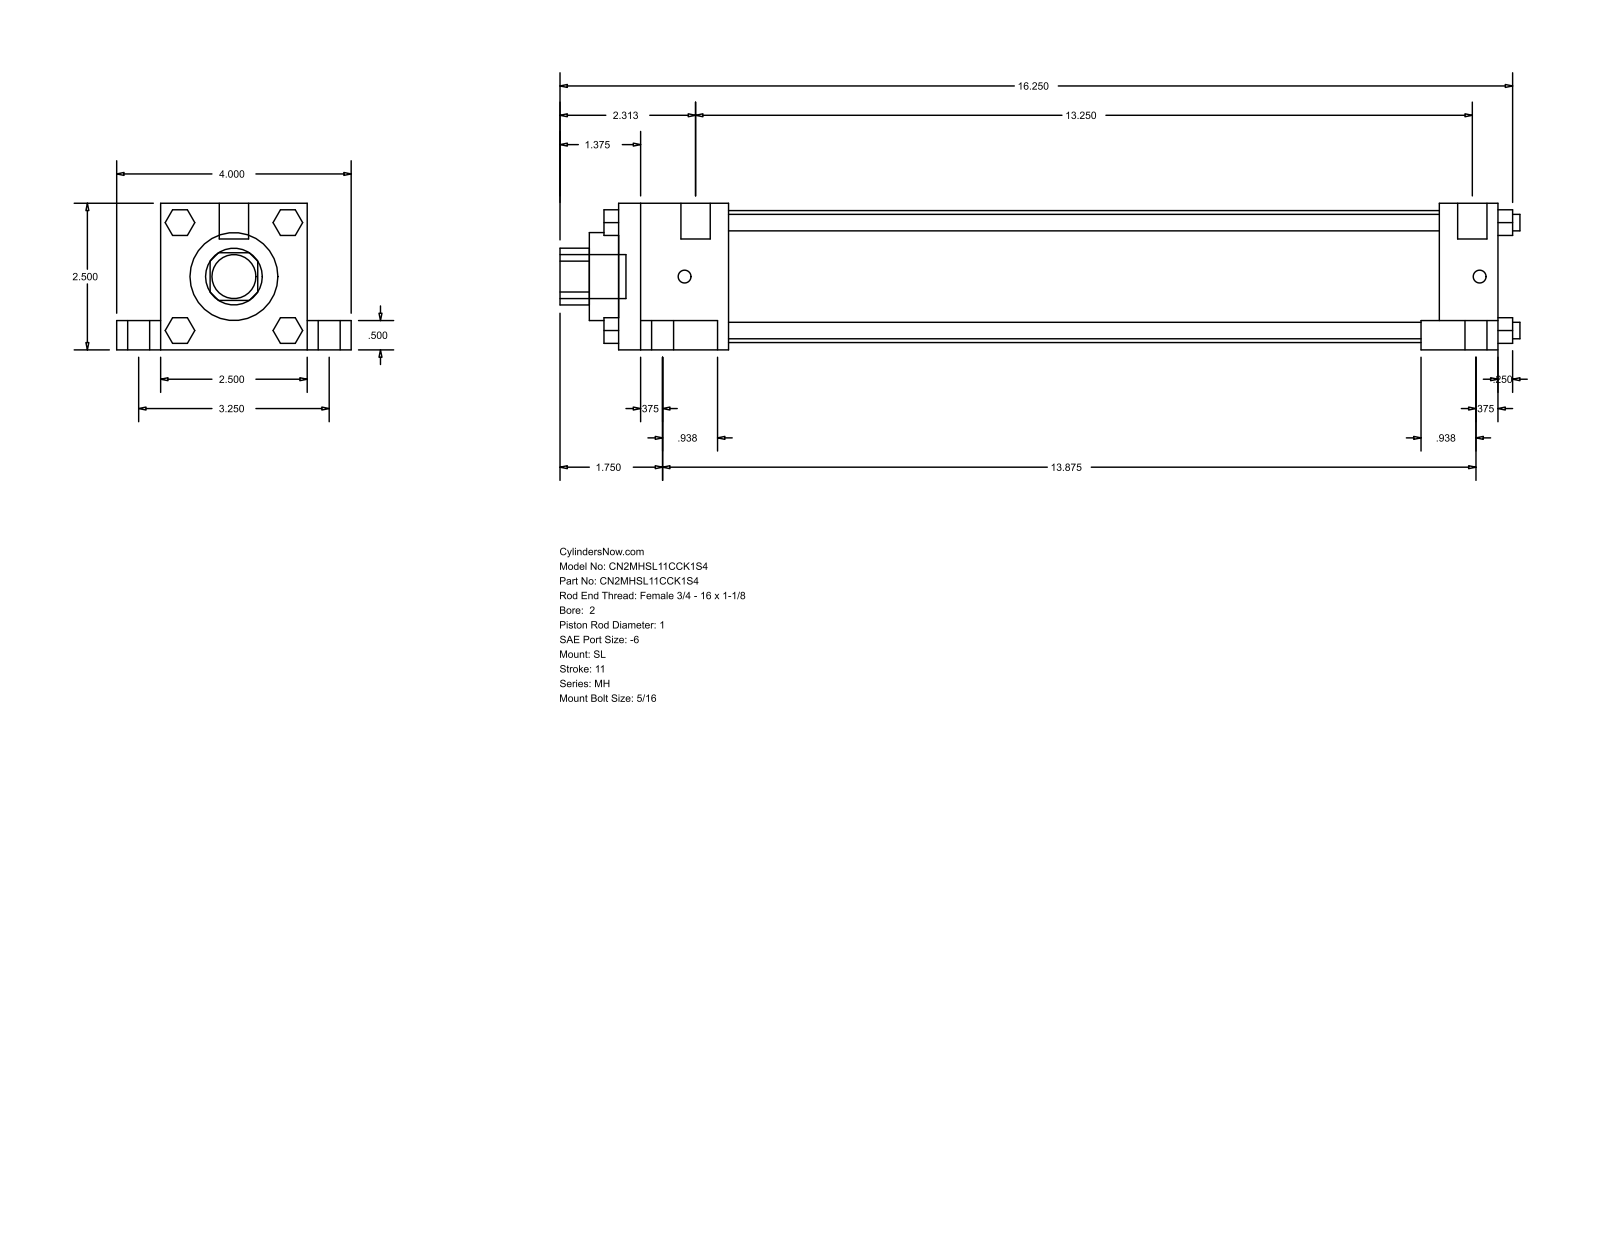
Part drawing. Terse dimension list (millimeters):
name: MH_SL__0200_1
written by: GSSL Pune (CONFIG_CONTROL_DESIGN)
unit: mm
bodies: 0 solids, 148 faces (112 planar, 36 cylindrical, 0 other)
size: 415.93 × 101.6 × 63.5
holes: 1× ⌀25.4, 1× ⌀38.1, 1× ⌀57.15
bosses: 4× ⌀15.88, 4× ⌀9.53, 4× ⌀7.14, 4× ⌀5.56, 2× ⌀12.7, 1× ⌀19.05
rounds: 1× R12.29
face distances: 63.5, 381, 12.7, 19.05, 50.8, 82.55, 25.4, 9.52, 355.6, 47.63
